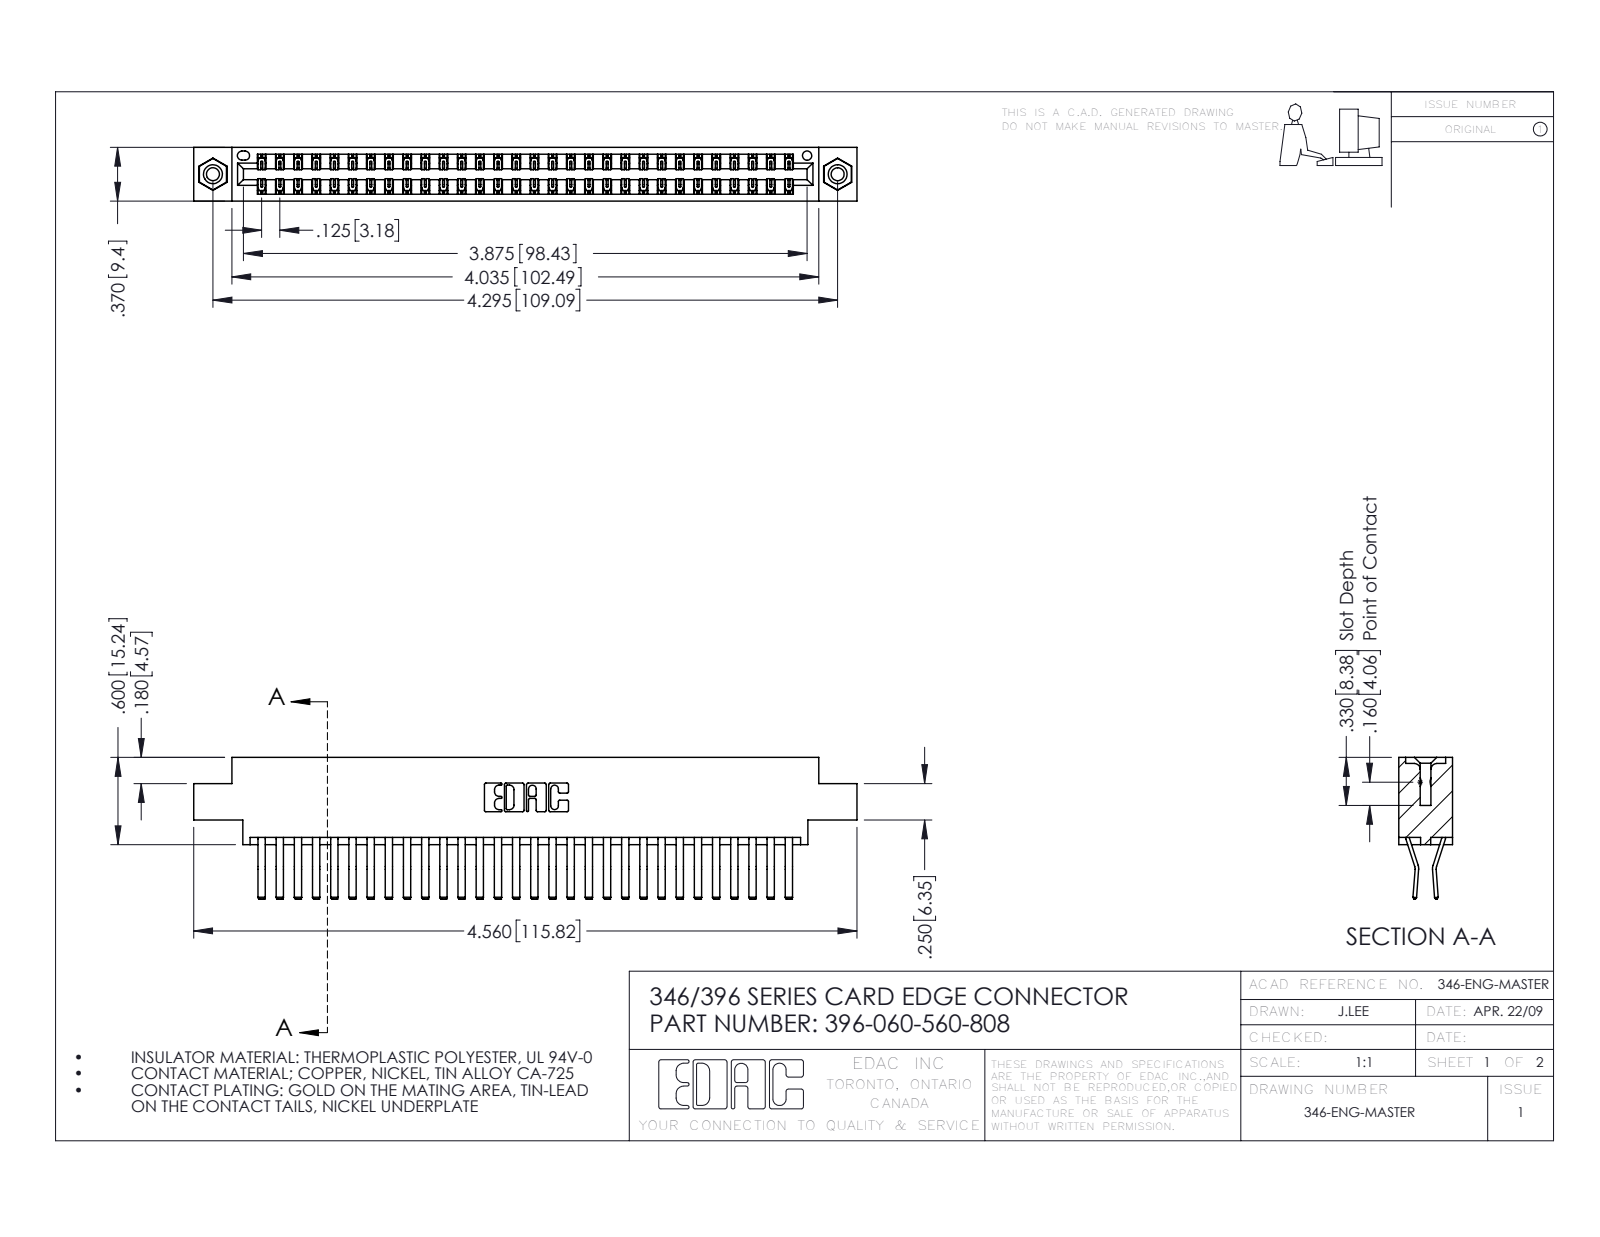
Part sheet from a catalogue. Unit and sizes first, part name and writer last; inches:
Units: inches
Overall size (bounding box): 4.56 × 0.975 × 0.37
Round holes (diameter × count): ⌀0.089 ×2, ⌀0.125 ×2, ⌀0.156 ×2, ⌀0.064 ×1
Round bosses / shafts (diameter × count): ⌀0.155 ×2
Partial cylindrical surfaces — rounded edges, fillets, slot ends (radius × count): R0.006 ×90, R0.01 ×22, R0.007 ×6, R0.031 ×6, R0.026 ×3, R0.01 ×2, R0.014 ×2, R0.022 ×2
Main face-to-face distances: 0.048, 0.322, 0.37, 0.025, 0.25, 0.072, 0.298, 0.275, 0.222, 0.148
Hole centre spacings: 0.246, 4.087, 4.295
Volume: 0.698 in³ · Surface area: 26 in²
Bodies: 63 solids, 3426 faces (2212 planar, 1198 cylindrical, 16 other)
Part name (STEP PRODUCT): 345-292-001_560 Tail; 346 Part_0.170 Offset - 0.156 Dia-TI; 345-250-001_345-250-003-102; 396-060-560-808
STEP written by: SolidWorks 2016 (CONFIG_CONTROL_DESIGN)
